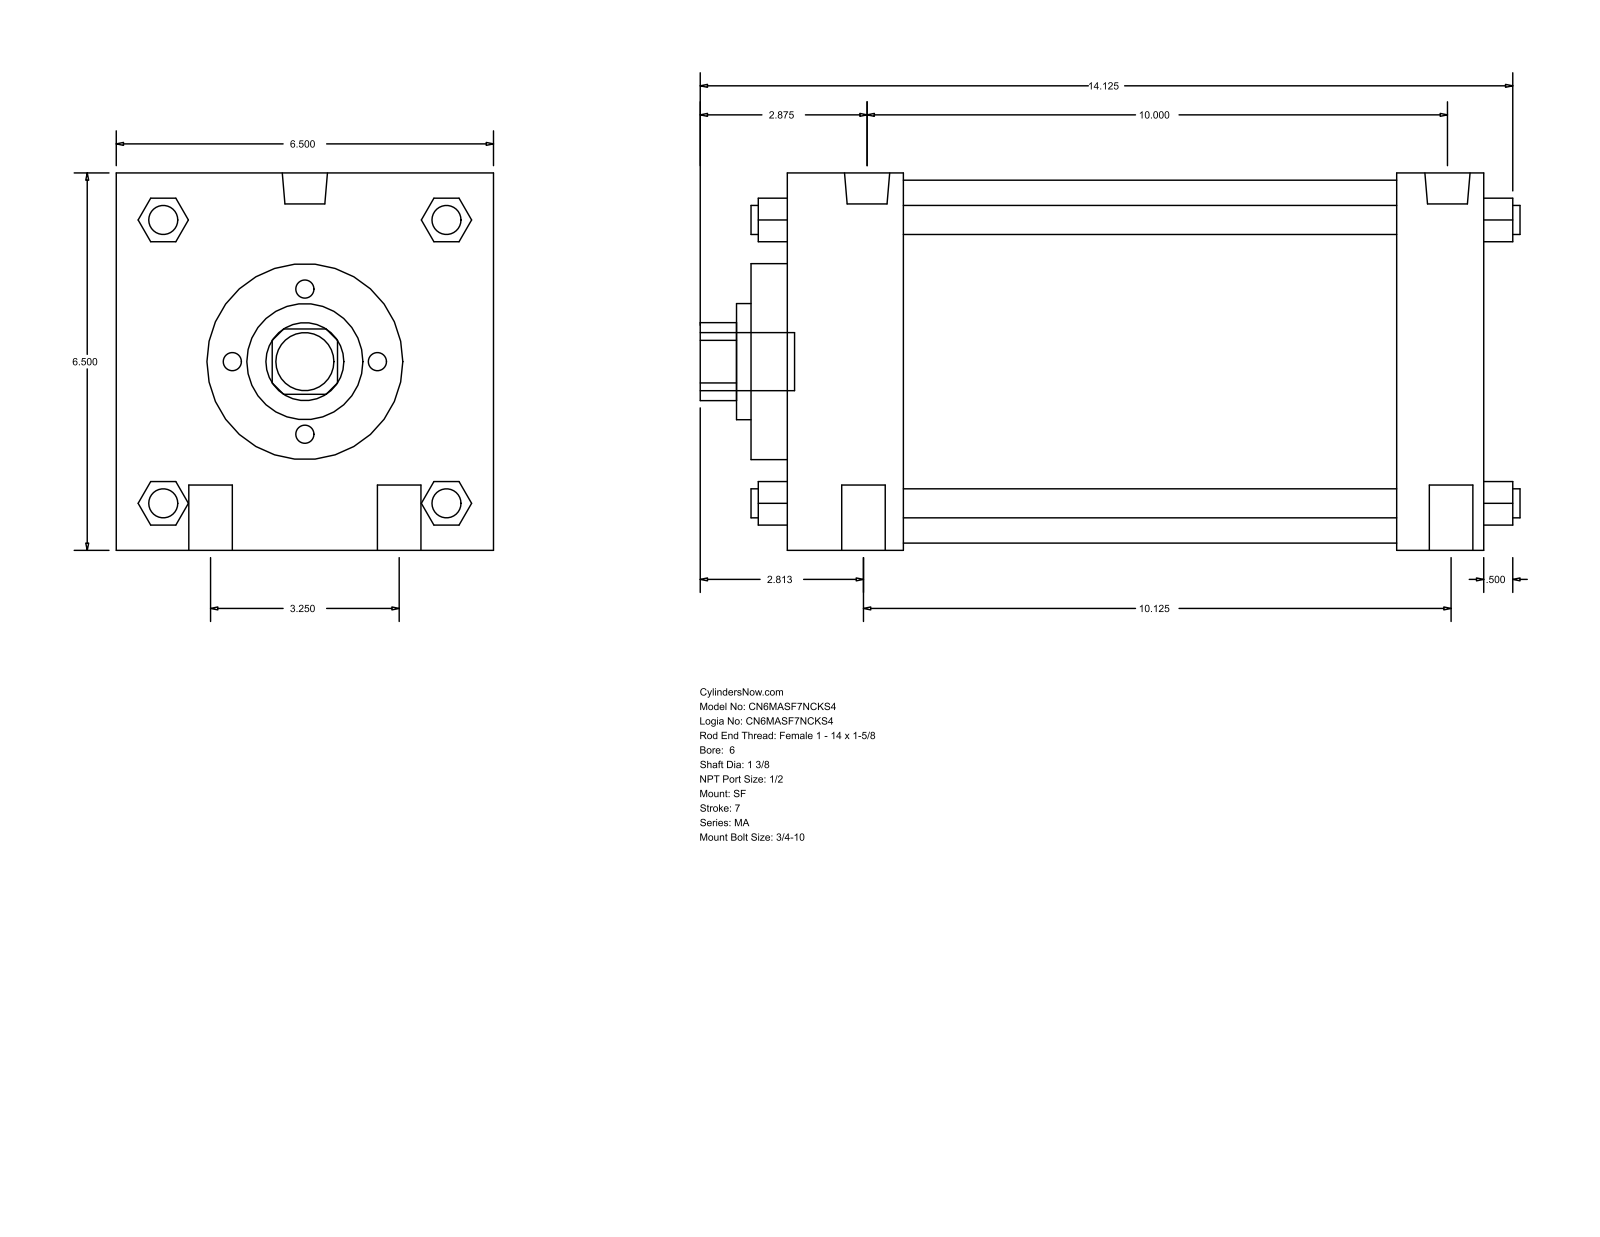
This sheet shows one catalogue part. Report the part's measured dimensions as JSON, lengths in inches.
{"part_name": "MA_SF__0600_1.375", "step_written_by": "GSSL Pune (CONFIG_CONTROL_DESIGN)", "units": "inches", "bodies": {"solids": 0, "faces": 126, "planar": 95, "cylindrical": 31, "other": 0}, "overall_size": [14.125, 6.5, 6.5], "round_holes": [[1.375, 1], [2, 1], [3.375, 1], [6.25, 1]], "round_bosses_or_shafts": [[0.75, 4], [0.5, 4], [0.778, 2], [0.687, 2], [1, 1]], "partial_cylinders_radius": [[0.672, 1]], "face_to_face_distances": [6.5, 12, 10.5, 2, 1.5, 8.5, 10, 0.625, 12.625, 2.625]}
